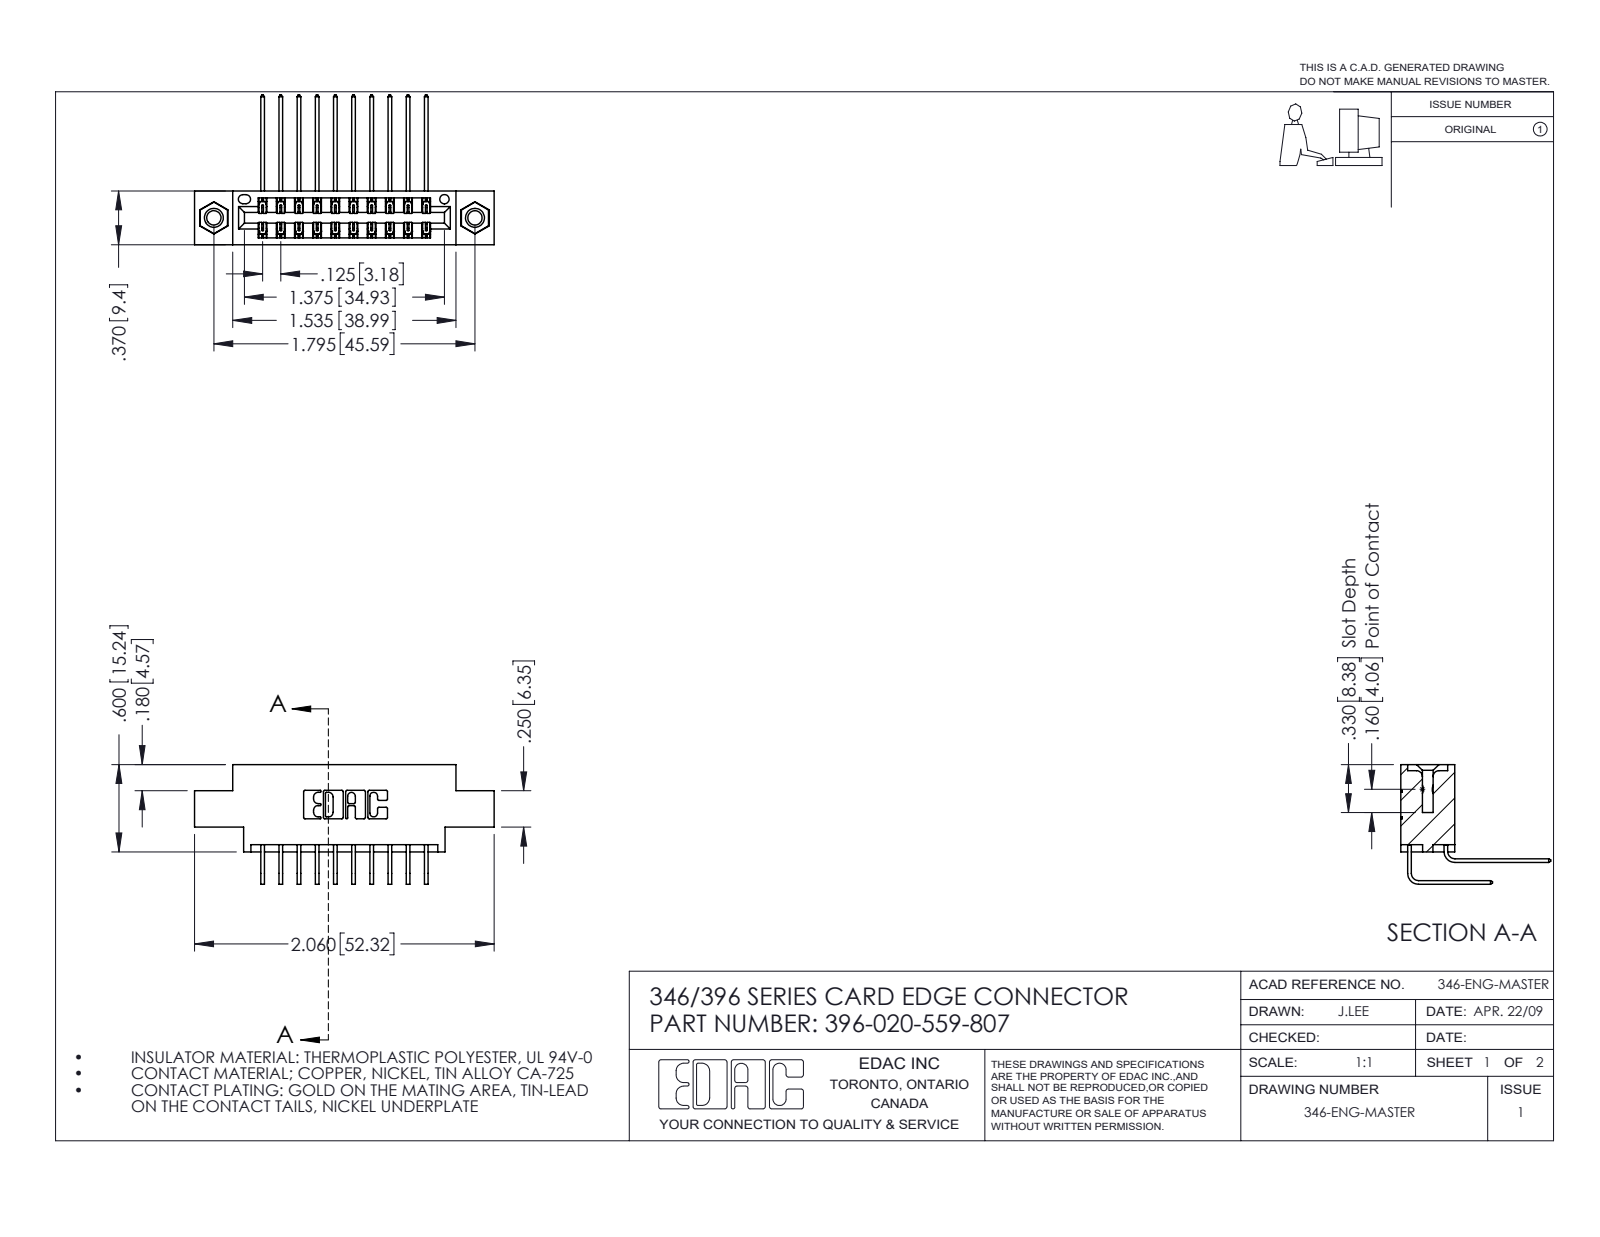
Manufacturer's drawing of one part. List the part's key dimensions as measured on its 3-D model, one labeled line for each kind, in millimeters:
Part name (STEP PRODUCT): 345-250-001_345-250-005-103; 346 Part_0.170 Offset - 0.156 Dia-TI; 396-020-559-807; 345-292-001_558 559 Tail - 1 (+1 more)
STEP written by: SolidWorks 2016 (CONFIG_CONTROL_DESIGN)
Units: millimetres
Bodies: 23 solids, 1266 faces (852 planar, 398 cylindrical, 16 other)
Overall size (bounding box): 52.3 × 26.2 × 20.9
Volume: 4 800 mm³ · Surface area: 6 865 mm²
Round holes (diameter × count): ⌀2.5 ×2, ⌀3.2 ×2, ⌀4 ×2, ⌀1.6 ×1
Round bosses / shafts (diameter × count): ⌀3.9 ×2
Partial cylindrical surfaces — rounded edges, fillets, slot ends (radius × count): R0.2 ×30, R0.3 ×22, R0.2 ×6, R0.8 ×6, R0.7 ×3, R0.4 ×2, R0.6 ×2, R0.6 ×2
Main face-to-face distances: 6.4, 1.2, 8.2, 9.4, 0.6, 1.8, 7.6, 5.6, 3.8, 7
Hole centre spacings: 6.2, 40.4, 45.6
